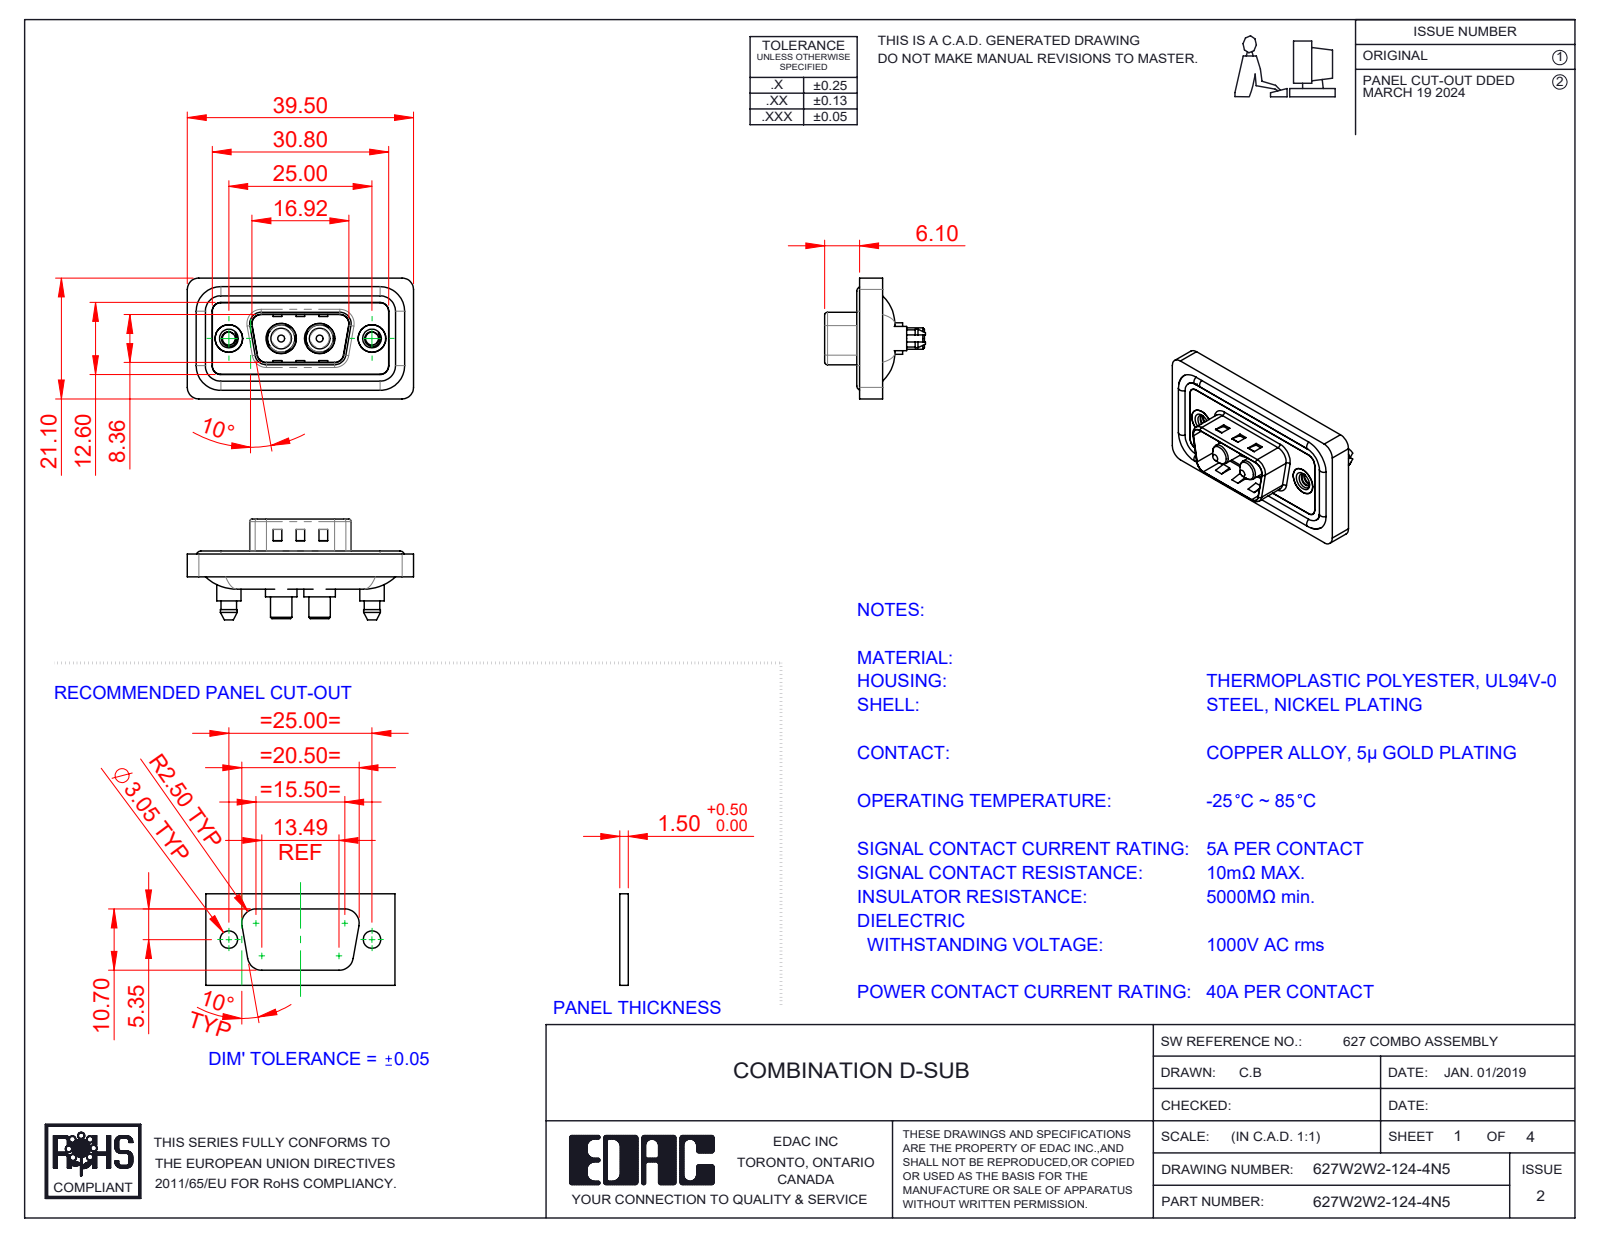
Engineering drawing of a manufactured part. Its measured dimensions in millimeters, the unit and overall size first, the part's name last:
Units: millimetres
Overall size (bounding box): 39.5 × 21.1 × 17.6
Round holes (diameter × count): ⌀2.26 ×2, ⌀4 ×2, ⌀4.8 ×2, ⌀4.85 ×2, ⌀5 ×2, ⌀5.3 ×2
Round bosses / shafts (diameter × count): ⌀1.6 ×4, ⌀5.5 ×2, ⌀5.4 ×2, ⌀5.2 ×2, ⌀4.9 ×2, ⌀4.75 ×2, ⌀4.25 ×2, ⌀3.75 ×2
Partial cylindrical surfaces — rounded edges, fillets, slot ends (radius × count): R1.5 ×24, R2 ×18, R1.6 ×10, R0.5 ×8, R0.25 ×4, R0.6 ×4, R0.65 ×4, R0.9 ×4
Main face-to-face distances: 0.4, 1.1, 2.9, 3.1, 0.5, 1.6, 1.5, 4, 0.7, 2.5
Hole centre spacings: 9.14, 15.86, 6.72, 25
Volume: 4 631 mm³ · Surface area: 7 339 mm²
Bodies: 11 solids, 539 faces (181 planar, 250 cylindrical, 108 other)
Part name (STEP PRODUCT): 627Combo Housing_2W2; Power Pin_40A S; 627Combo Shell Front_09 Contacts; 627Combo Threaded Boardlock_5 (+3 more)
STEP written by: SolidWorks 2023 (CONFIG_CONTROL_DESIGN)
